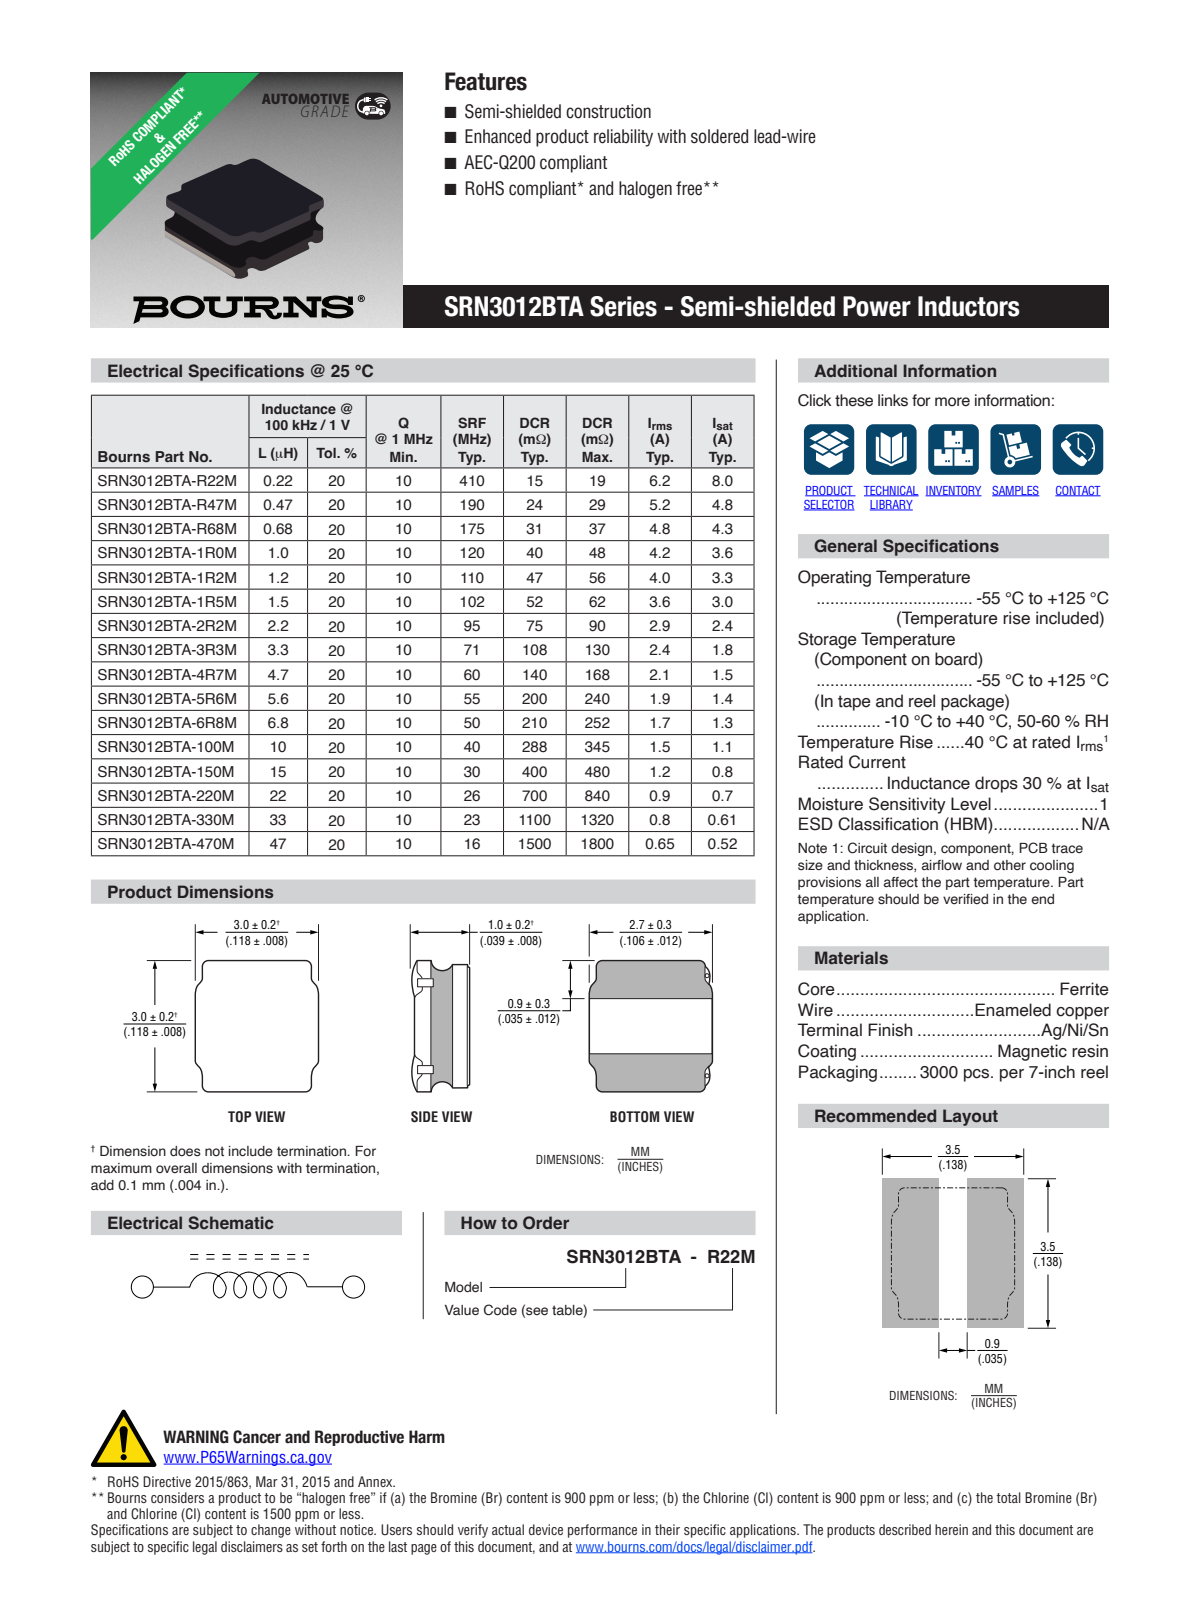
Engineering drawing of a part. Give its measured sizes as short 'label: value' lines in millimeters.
name: HPC3012BM
written by: SIEMENS PLM Software NX 1980 (AUTOMOTIVE_DESIGN)
unit: mm
bodies: 7 solids, 192 faces (47 planar, 25 cylindrical, 120 other)
size: 2.95 × 2.95 × 1.12
volume: 8 mm³; area: 93 mm²
holes: 1× ⌀1.55
bosses: 1× ⌀2.69, 1× ⌀1.6
rounds: 1× R1.38, 1× R1.38
face distances: 0.73, 0.32, 0.41, 1.05, 0.71, 1.03, 0.39, 0.8, 1.12, 0.63
